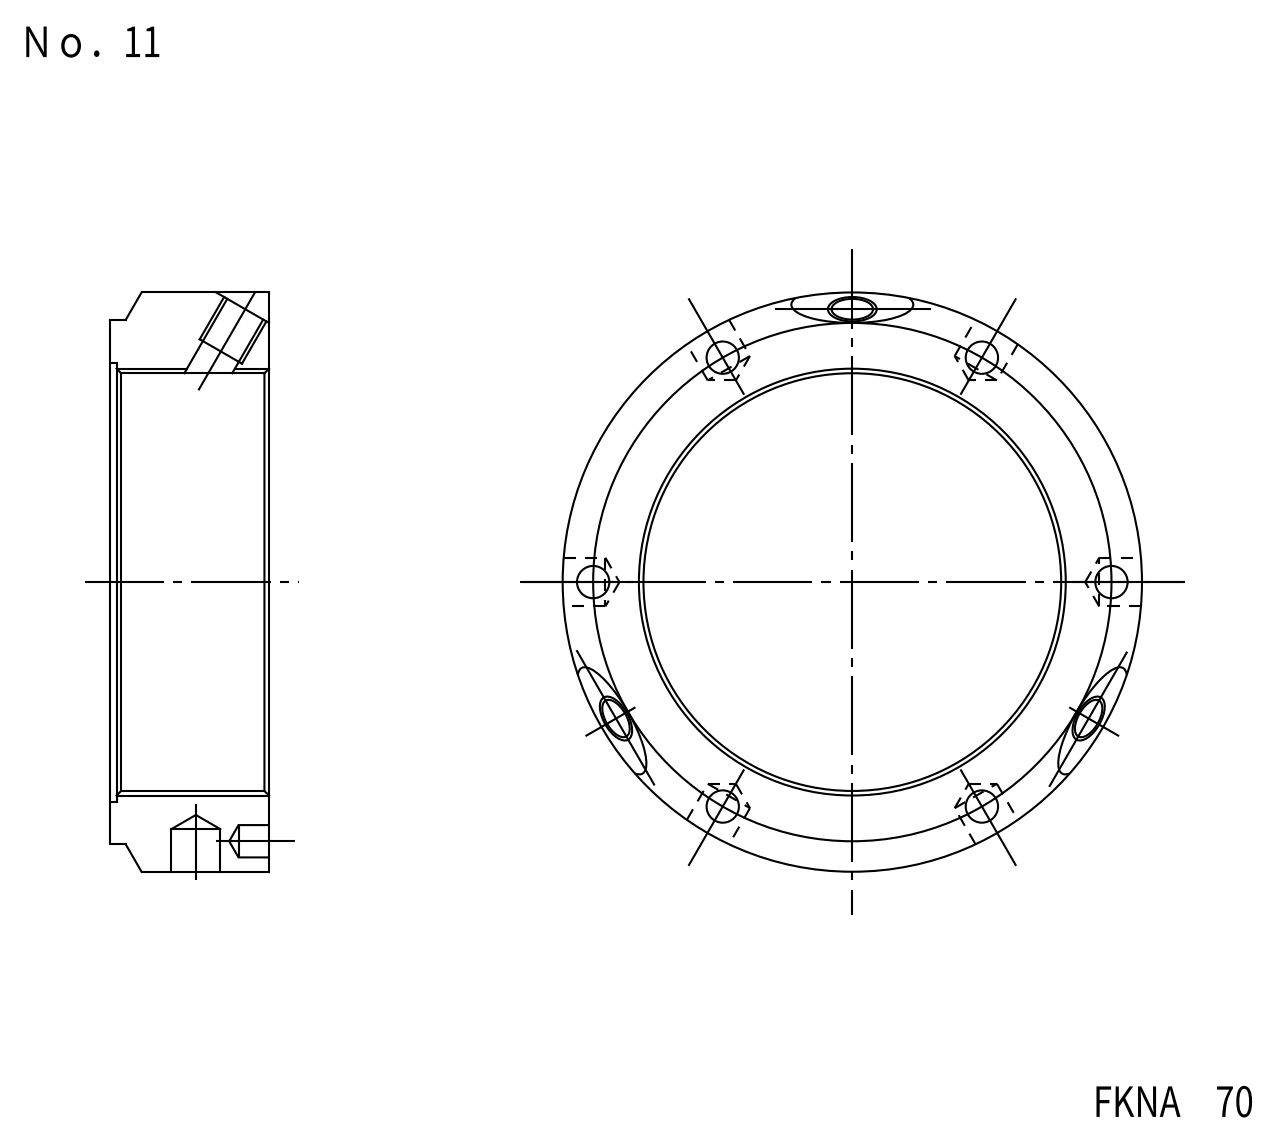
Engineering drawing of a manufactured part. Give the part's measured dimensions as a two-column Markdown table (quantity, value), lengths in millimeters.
| quantity | value |
| --- | --- |
| part name | FKD FKNA70 |
| STEP written by | Autodesk Inventor LT (CONFIG_CONTROL_DESIGN) |
| units | millimeters |
| bodies | 1 solid, 44 faces (6 planar, 25 cylindrical, 13 other) |
| overall size | 95 × 95 × 26 |
| volume | 76 142 mm³ |
| surface area | 21 221 mm² |
| round holes (diameter × count) | 5.3 × 6, 6.65 × 3, 8 × 3, 8.2 × 3, 70 × 1, 72 × 1 |
| round bosses / shafts (diameter × count) | 95 × 1, 86 × 1 |
| partial cylindrical surfaces (radius × count) | 20 × 3 |
| main face-to-face distances | 26, 1.5, 24.5 |
| hole center spacings | 42.5, 73.61, 73.62, 85.01, 85 |
